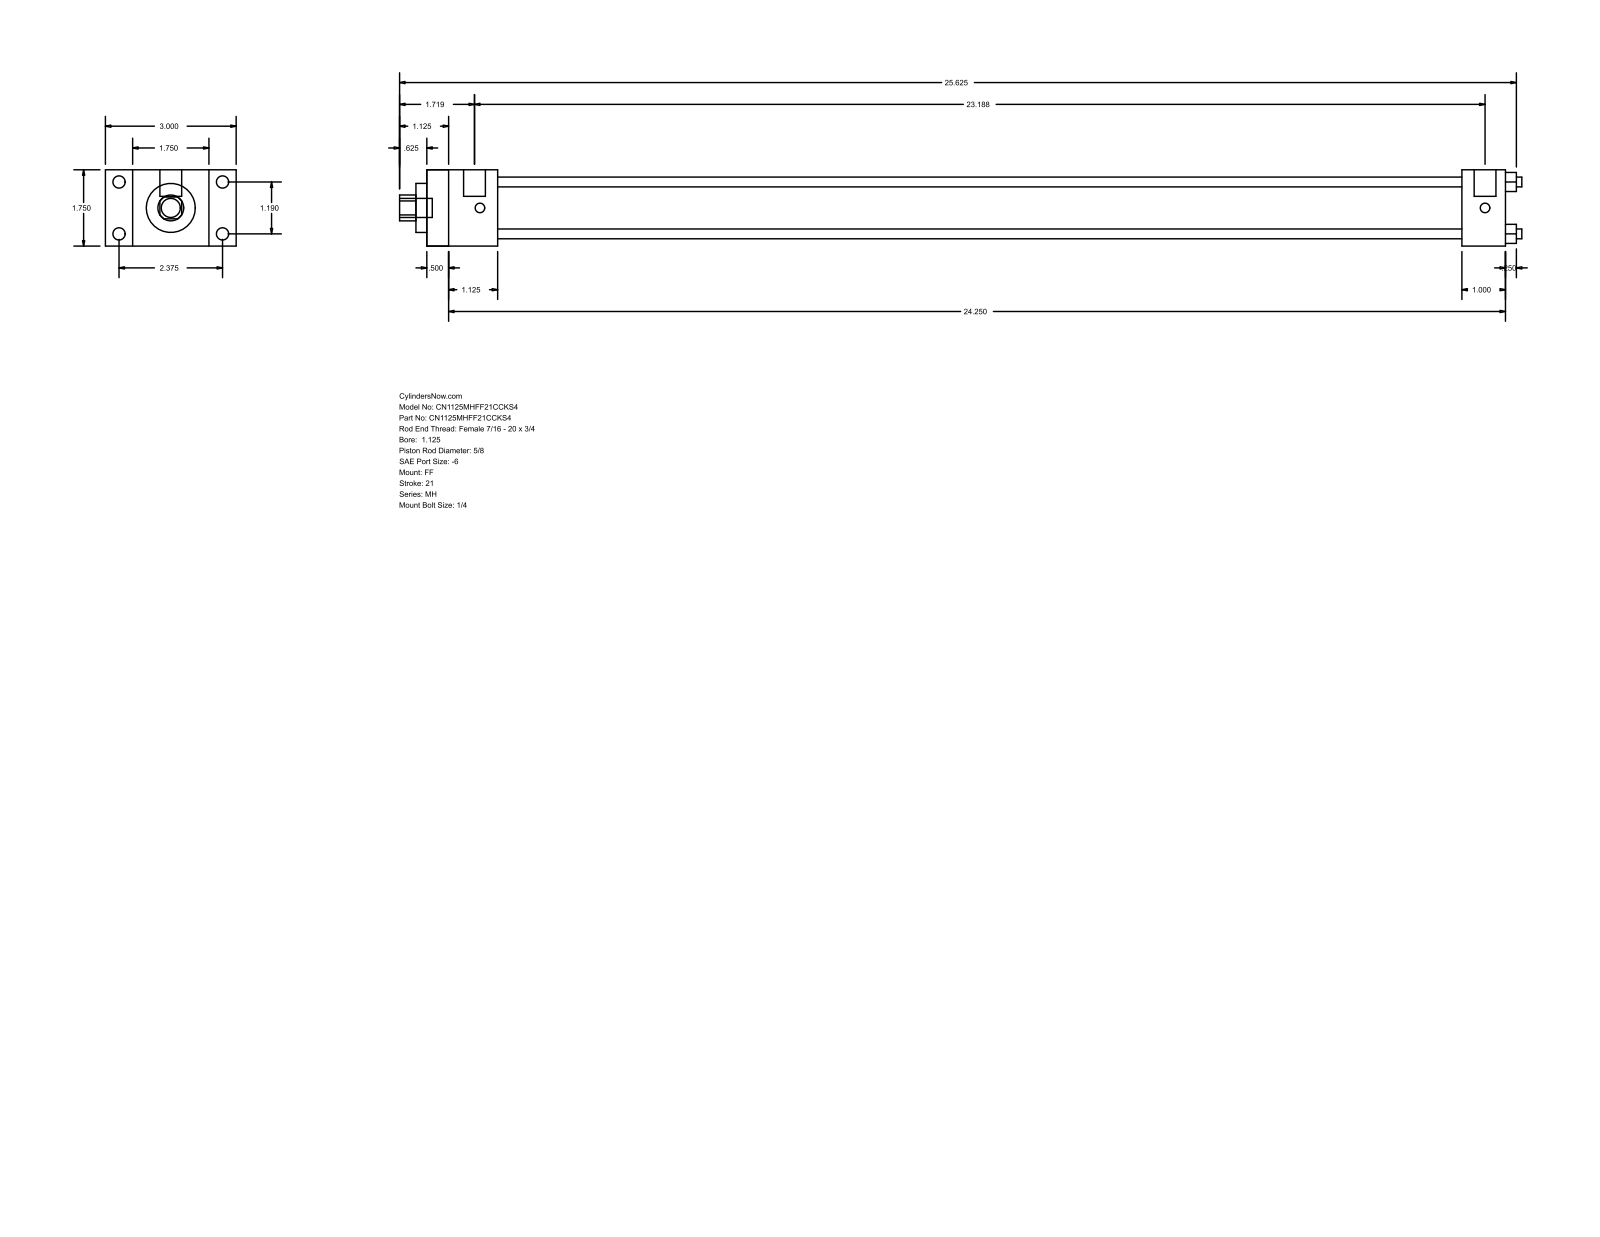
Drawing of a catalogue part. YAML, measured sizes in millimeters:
part_name: "MH_FF__0112_0.625"
step_written_by: "GSSL Pune (CONFIG_CONTROL_DESIGN)"
units: millimeters
bodies: {solids: 0, faces: 92, planar: 64, cylindrical: 28, other: 0}
overall_size: [654.05, 76.2, 44.45]
round_holes:
  - {diameter: 5.71, count: 4}
  - {diameter: 15.88, count: 1}
  - {diameter: 28.57, count: 1}
  - {diameter: 34.92, count: 1}
round_bosses_or_shafts:
  - {diameter: 7.14, count: 4}
  - {diameter: 5.56, count: 4}
  - {diameter: 12.7, count: 2}
  - {diameter: 11.11, count: 1}
partial_cylinders:
  - {radius: 7.54, count: 1}
face_to_face_distances: [44.46, 628.64, 12.69, 615.95, 15.87, 60.33, 28.58, 41.27, 603.24, 590.55]
hole_center_spacings: [21.37, 30.22, 42.74]
